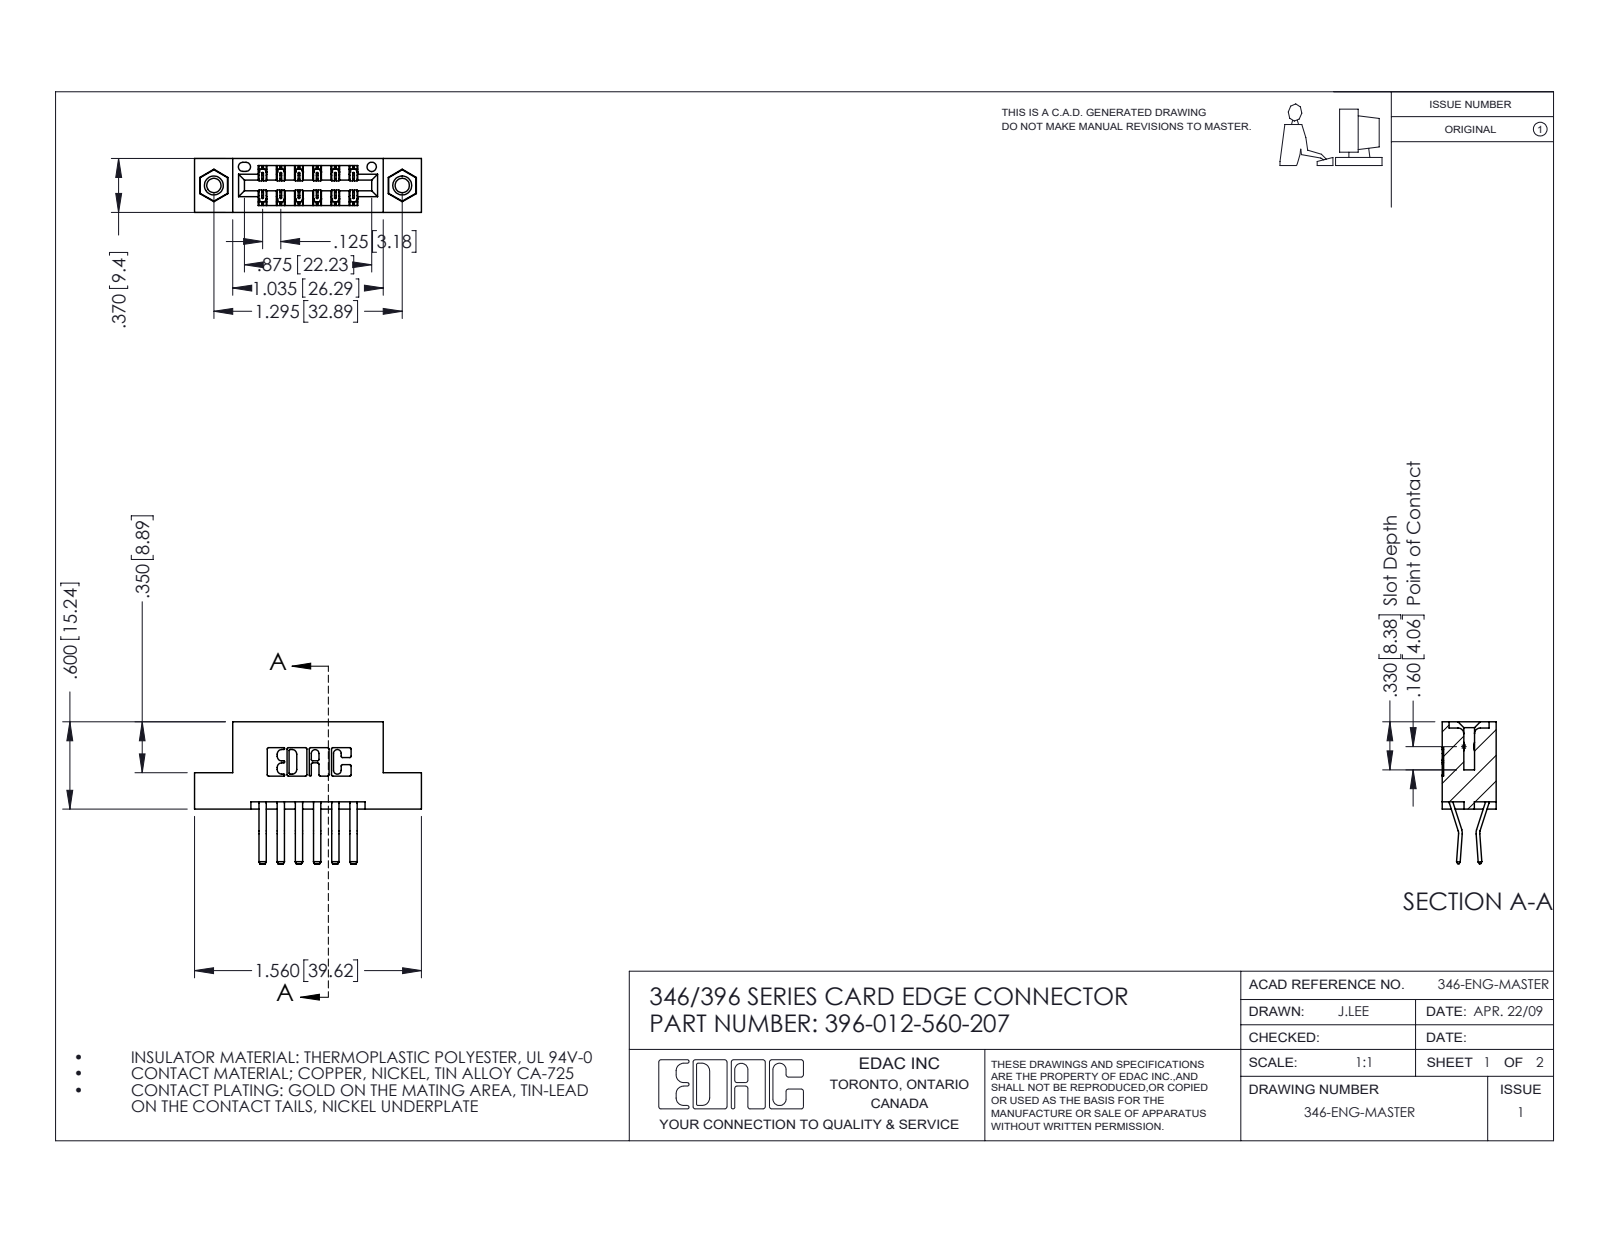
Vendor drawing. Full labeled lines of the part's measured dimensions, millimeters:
Part name (STEP PRODUCT): 346 Part_Flush Mounting Lugs - 0.156 Dia-TI; 345-292-001_560 Tail; 396-012-560-207; 345-250-001_345-250-005-103
STEP written by: SolidWorks 2016 (CONFIG_CONTROL_DESIGN)
Units: millimetres
Bodies: 15 solids, 830 faces (528 planar, 286 cylindrical, 16 other)
Overall size (bounding box): 39.6 × 24.8 × 9.4
Volume: 3 650 mm³ · Surface area: 4 694 mm²
Round holes (diameter × count): ⌀2.5 ×2, ⌀3.2 ×2, ⌀4 ×2, ⌀1.6 ×1
Round bosses / shafts (diameter × count): ⌀3.9 ×2
Partial cylindrical surfaces — rounded edges, fillets, slot ends (radius × count): R0.3 ×22, R0.2 ×18, R0.2 ×6, R0.8 ×6, R0.7 ×3, R0.3 ×2, R0.4 ×2, R0.6 ×2
Main face-to-face distances: 6.4, 9.4, 1.2, 8.2, 0.6, 3.2, 3.8, 5.6, 2.5, 4.4
Hole centre spacings: 6.2, 27.7, 32.9
